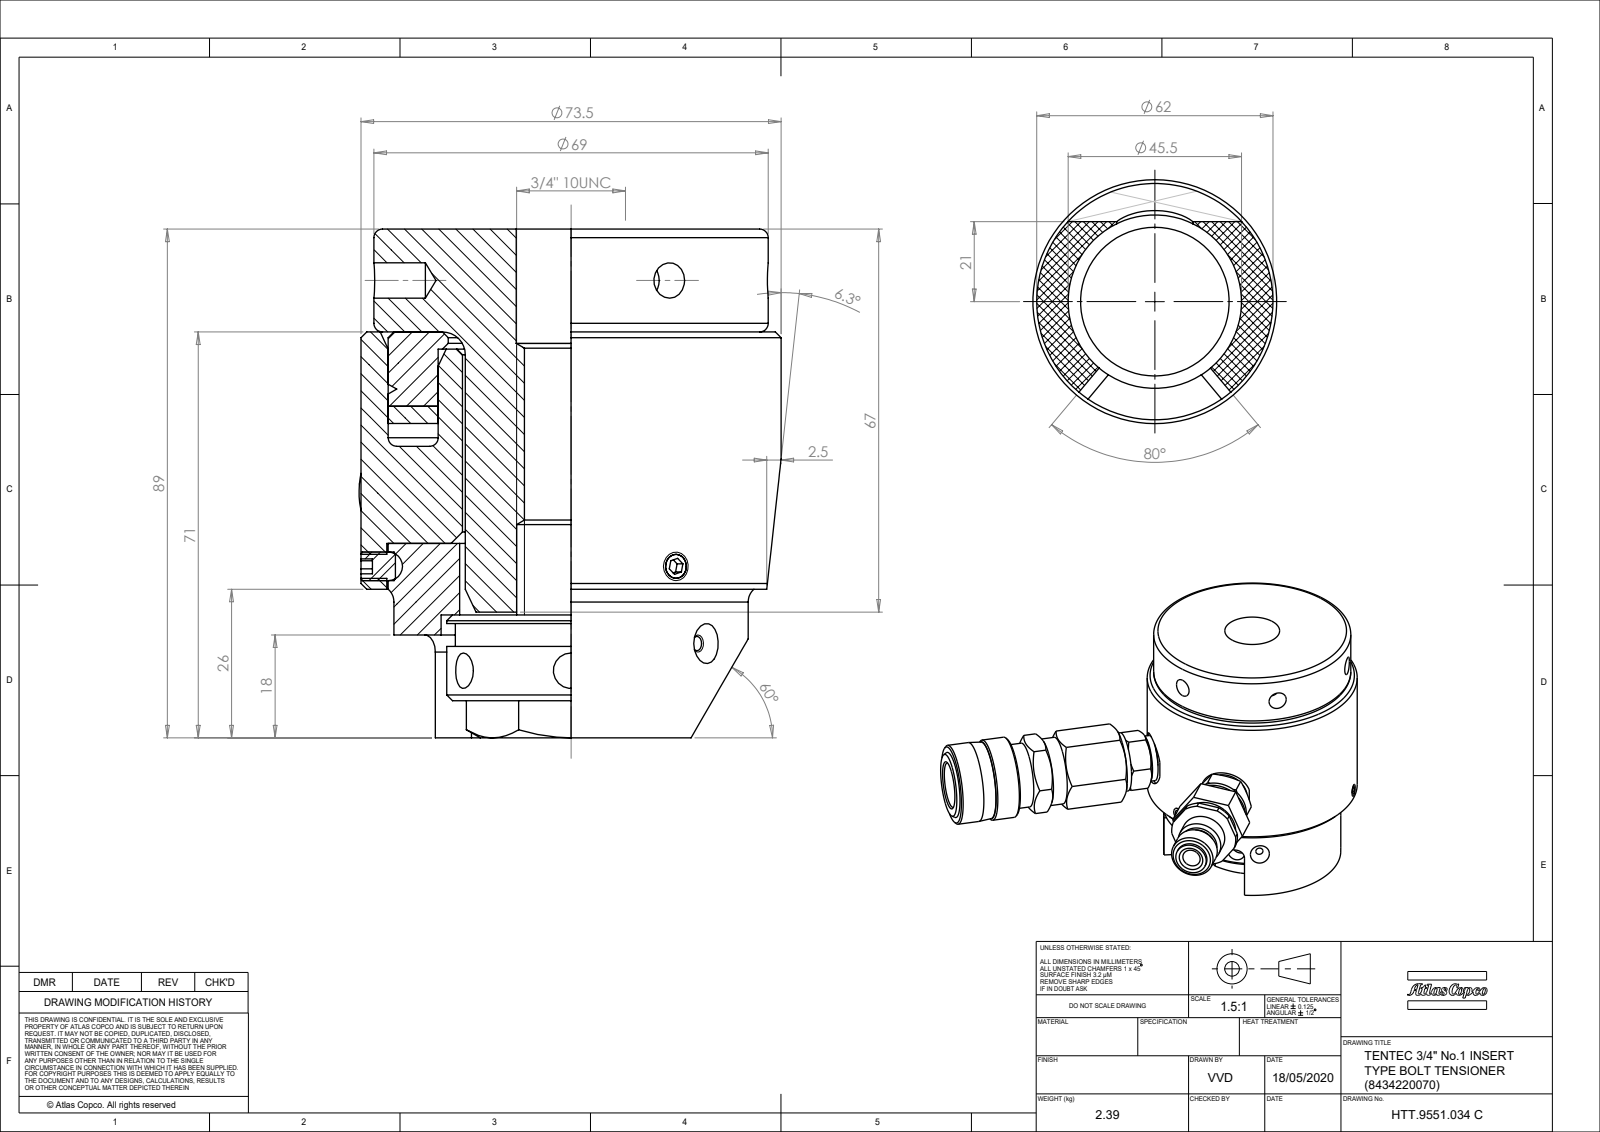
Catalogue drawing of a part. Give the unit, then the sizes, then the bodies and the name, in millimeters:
Units: millimetres
Overall size (bounding box): 137.8 × 113.3 × 89
Round holes (diameter × count): ⌀6.2 ×6, ⌀2.5 ×4, ⌀15 ×1, ⌀15.6 ×1, ⌀19.2 ×1, ⌀45.5 ×1
Round bosses / shafts (diameter × count): ⌀20.6 ×2, ⌀15.9 ×2, ⌀12 ×2, ⌀73.5 ×1, ⌀69 ×1, ⌀62 ×1, ⌀43.5 ×1, ⌀40.5 ×1
Partial cylindrical surfaces — rounded edges, fillets, slot ends (radius × count): R6 ×6, R3 ×2, R9 ×2, R11.6 ×1, R12.5 ×1, R16.8 ×1
Main face-to-face distances: 89, 18, 4, 71, 2, 26, 45, 63, 24, 22
Hole centre spacings: 31.2
Volume: 353 800 mm³ · Surface area: 51 600 mm²
Bodies: 1 solid, 346 faces (109 planar, 117 cylindrical, 120 other)
Part name (STEP PRODUCT): CTST_01-0_75_INCH_843_SW0001
STEP written by: CREO PARAMETRIC BY PTC INC, 2020281 (CONFIG_CONTROL_DESIGN)
